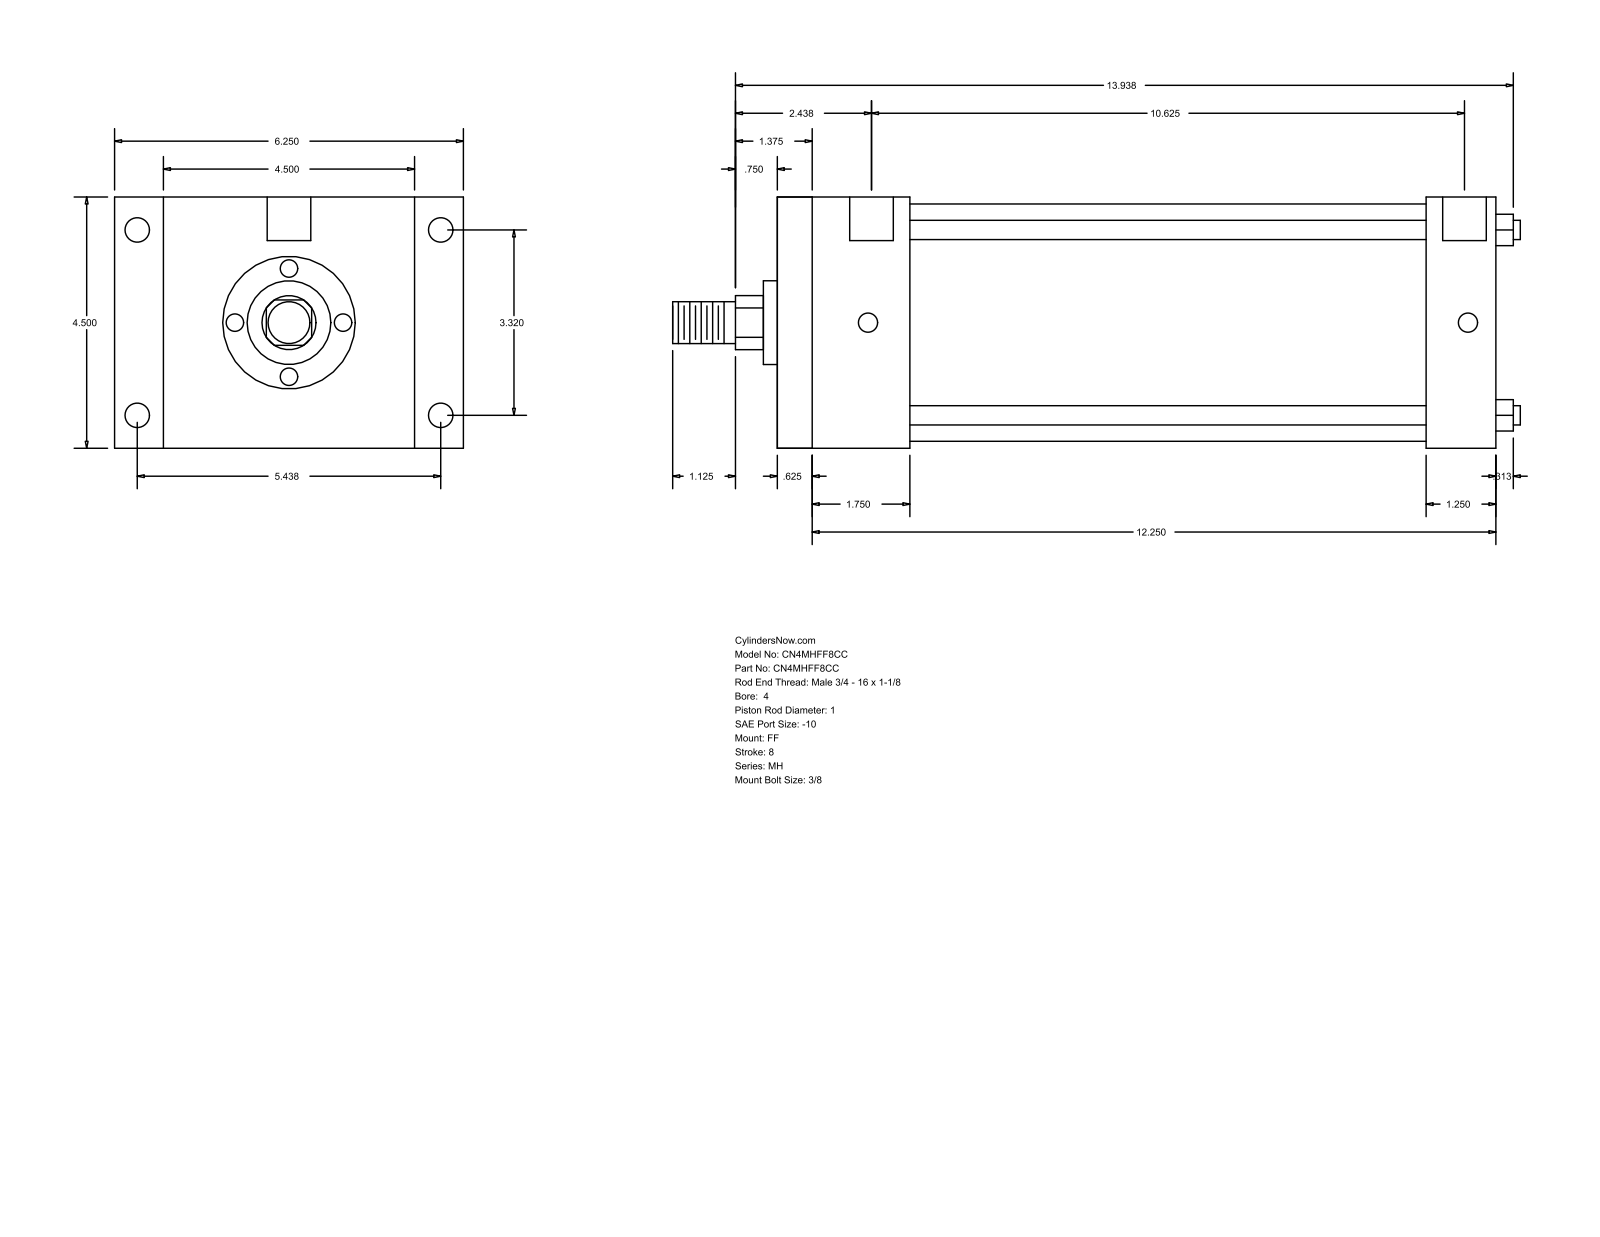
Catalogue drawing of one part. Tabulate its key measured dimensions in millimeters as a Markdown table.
| quantity | value |
| --- | --- |
| part name | MH_FF__0400_1 |
| STEP written by | GSSL Pune (CONFIG_CONTROL_DESIGN) |
| units | millimeters |
| bodies | 0 solids, 92 faces (64 planar, 28 cylindrical, 0 other) |
| overall size | 385.76 × 158.75 × 114.3 |
| round holes (diameter × count) | 8.73 × 4, 11.13 × 4, 19.84 × 2 |
| round bosses / shafts (diameter × count) | 8.76 × 4, 107.95 × 1, 38.1 × 1, 25.4 × 1, 19.05 × 1 |
| partial cylindrical surfaces (radius × count) | 12.29 × 1 |
| main face-to-face distances | 114.3, 327.02, 15.87, 311.15, 60.33, 44.46, 266.69, 295.27, 279.4, 234.94 |
| hole center spacings | 84.32, 138.12, 161.82, 273.05, 1.58, 1.59, 269.88, 271.46 |
